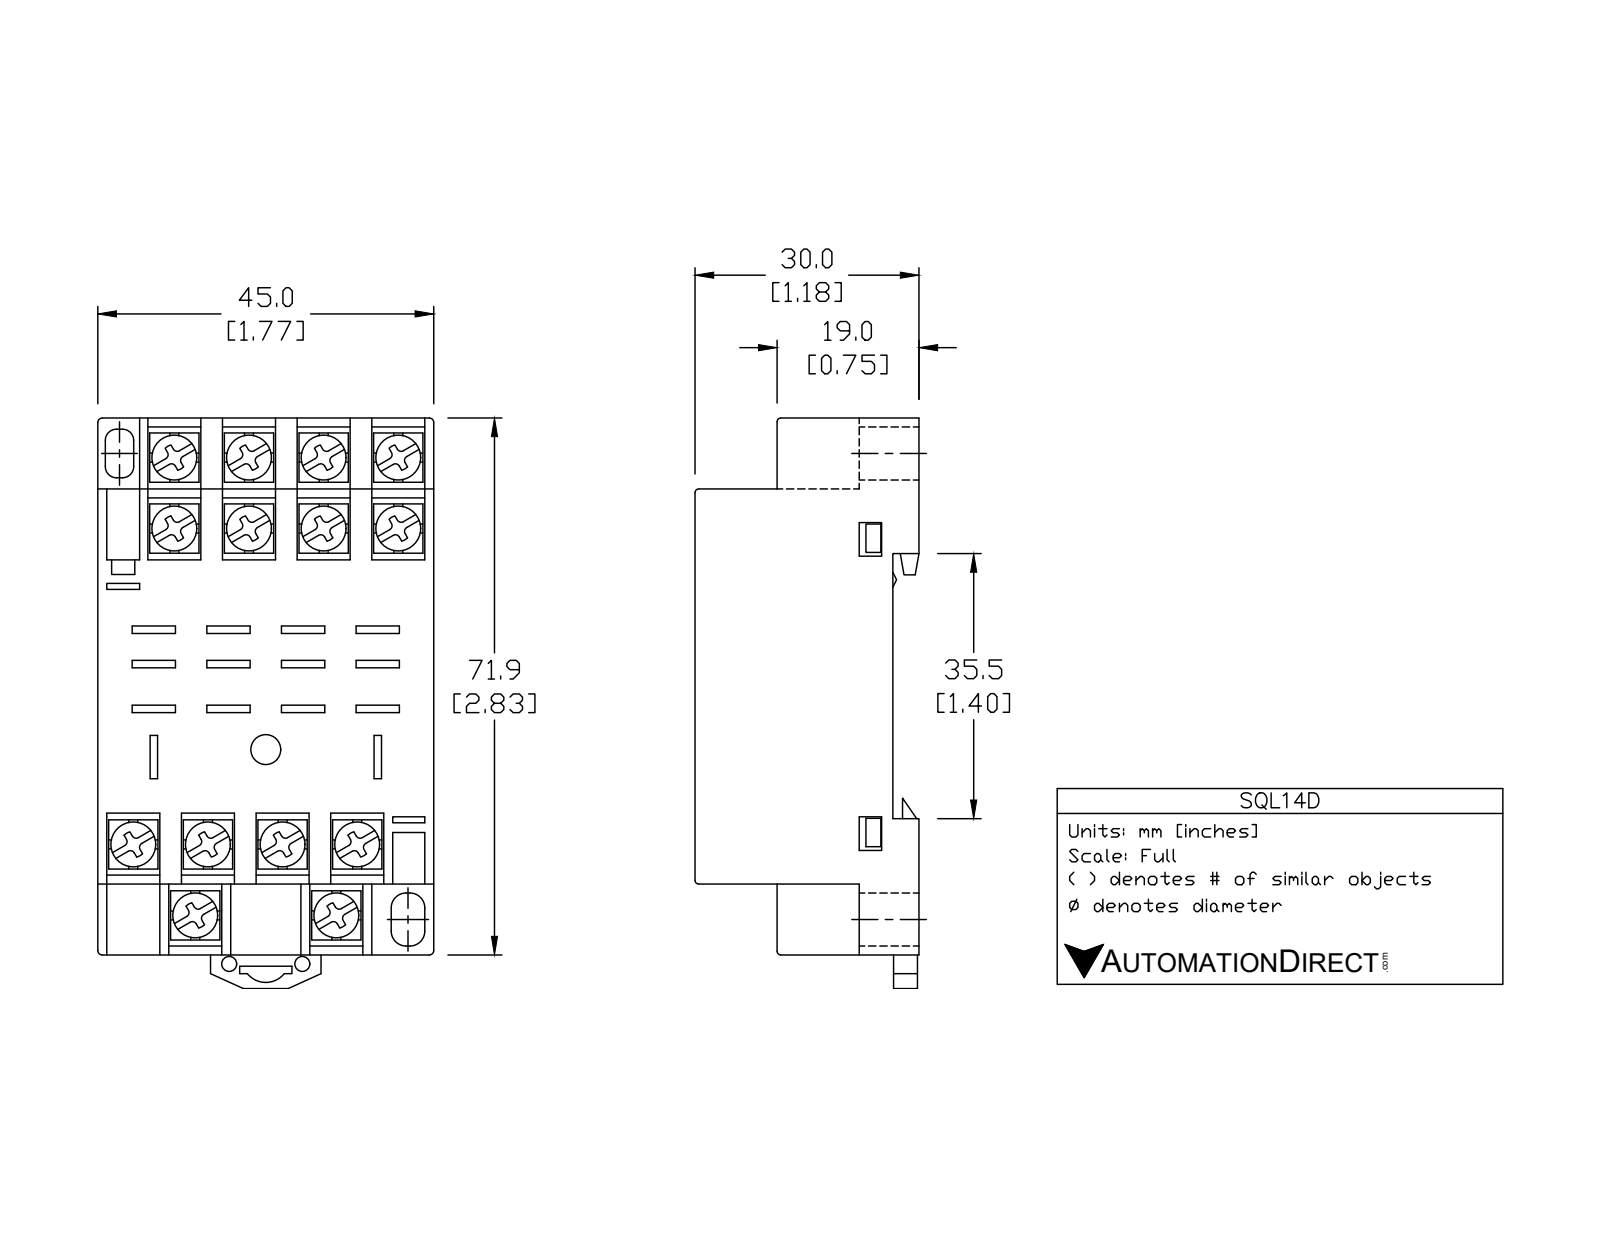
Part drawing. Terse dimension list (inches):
name: SQL14D
written by: SolidWorks 2013 (AUTOMOTIVE_DESIGN)
unit: in
bodies: 2 solids, 634 faces (544 planar, 62 cylindrical, 28 other)
size: 2.959 × 1.772 × 1.181
volume: 4.289 in³; area: 31.87 in²
bosses: 10× ⌀0.256, 4× ⌀0.256
rounds: 8× R0.039, 8× R0.059
face distances: 1.181, 1.772, 0.138, 0.181, 1.043, 0.039, 0.374, 0.394, 2.083, 0.402
